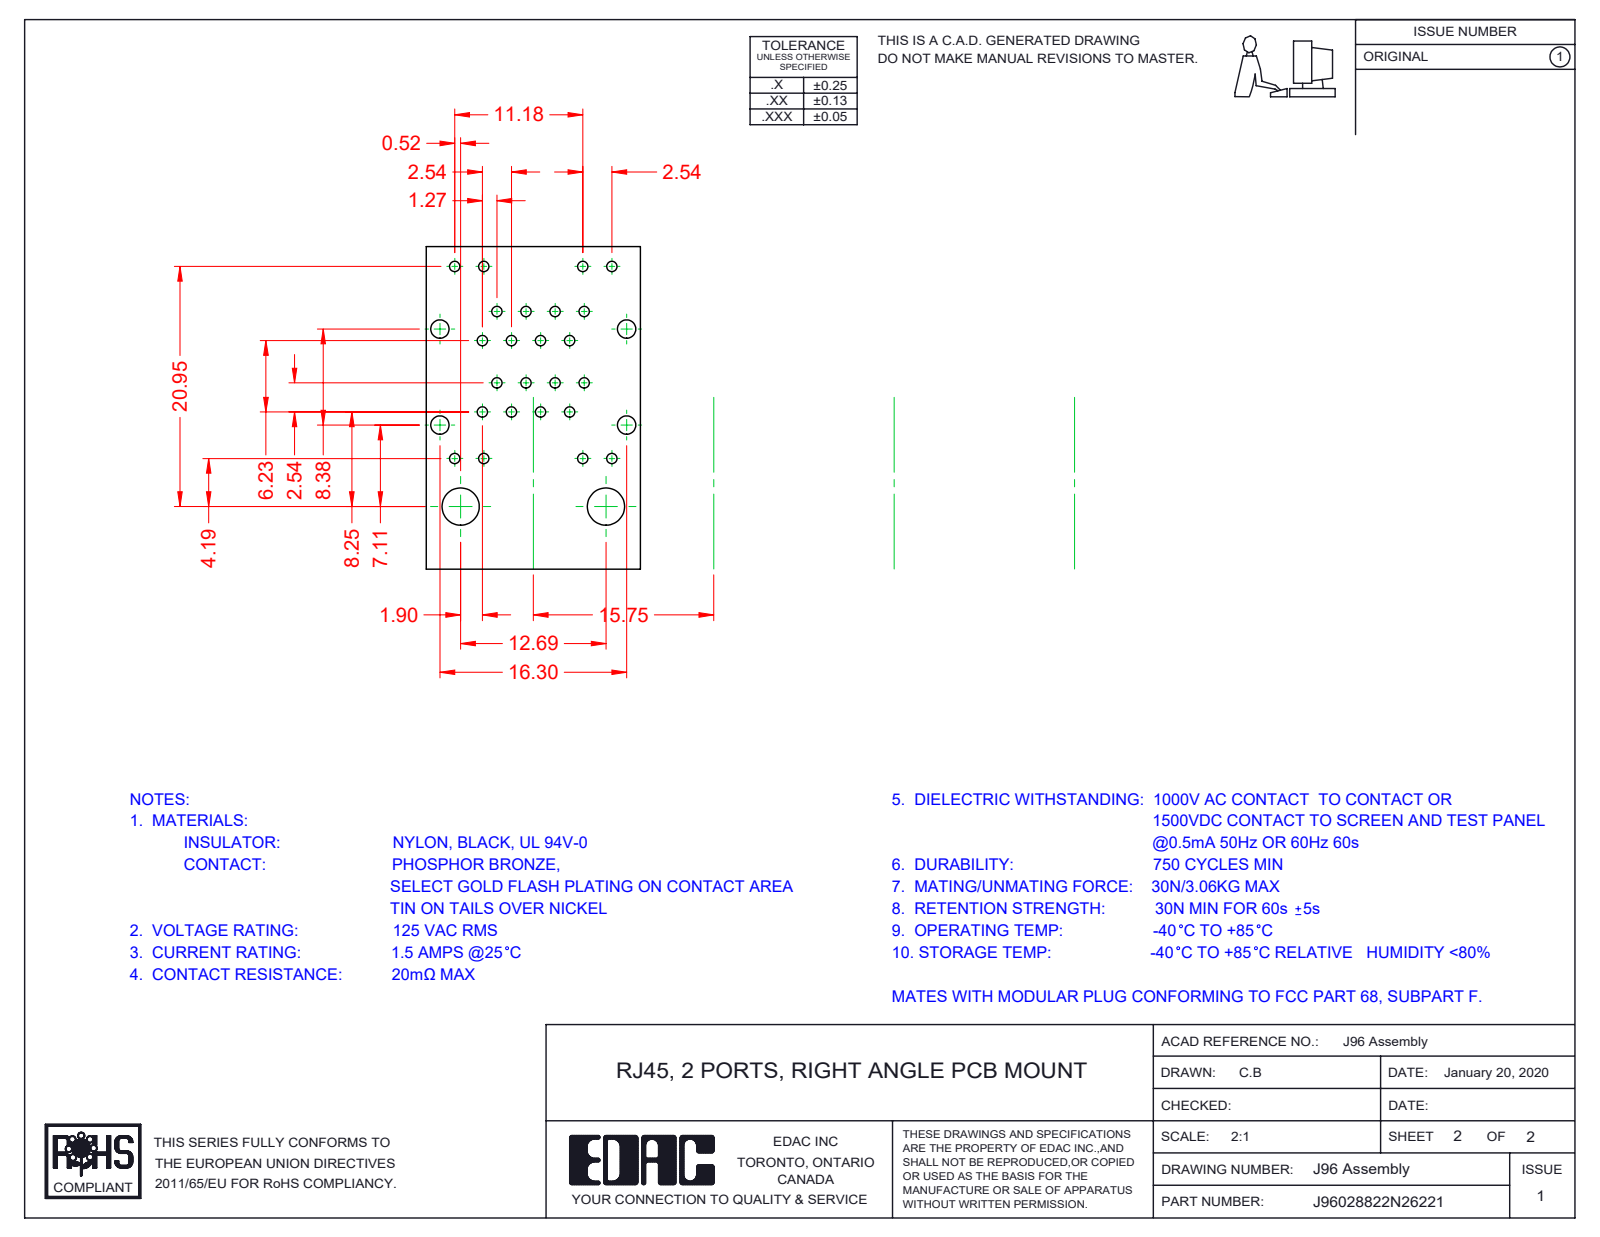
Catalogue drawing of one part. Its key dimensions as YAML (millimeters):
part_name: "96 Contacts Upper; 96 Grounding_2 Ports; 96 Contact Lock Upper; 96 Shield_2 Ports LED - EMI (+8 more)"
step_written_by: "SolidWorks 2016 (CONFIG_CONTROL_DESIGN)"
units: millimeters
bodies: {solids: 27, faces: 2421, planar: 1865, cylindrical: 450, other: 106}
overall_size: [31.38, 28.68, 16.8]
volume: 6849
surface_area: 19094
partial_cylinders:
  - {radius: 0.25, count: 48}
  - {radius: 0.15, count: 32}
  - {radius: 0.35, count: 24}
  - {radius: 0.5, count: 16}
  - {radius: 1, count: 16}
  - {radius: 0.2, count: 14}
  - {radius: 0.7, count: 9}
  - {radius: 2, count: 5}
face_to_face_distances: [16.3, 16.1, 1.75, 16.5, 14.75, 1.55, 14.55, 0.53, 1.48, 11.2]
